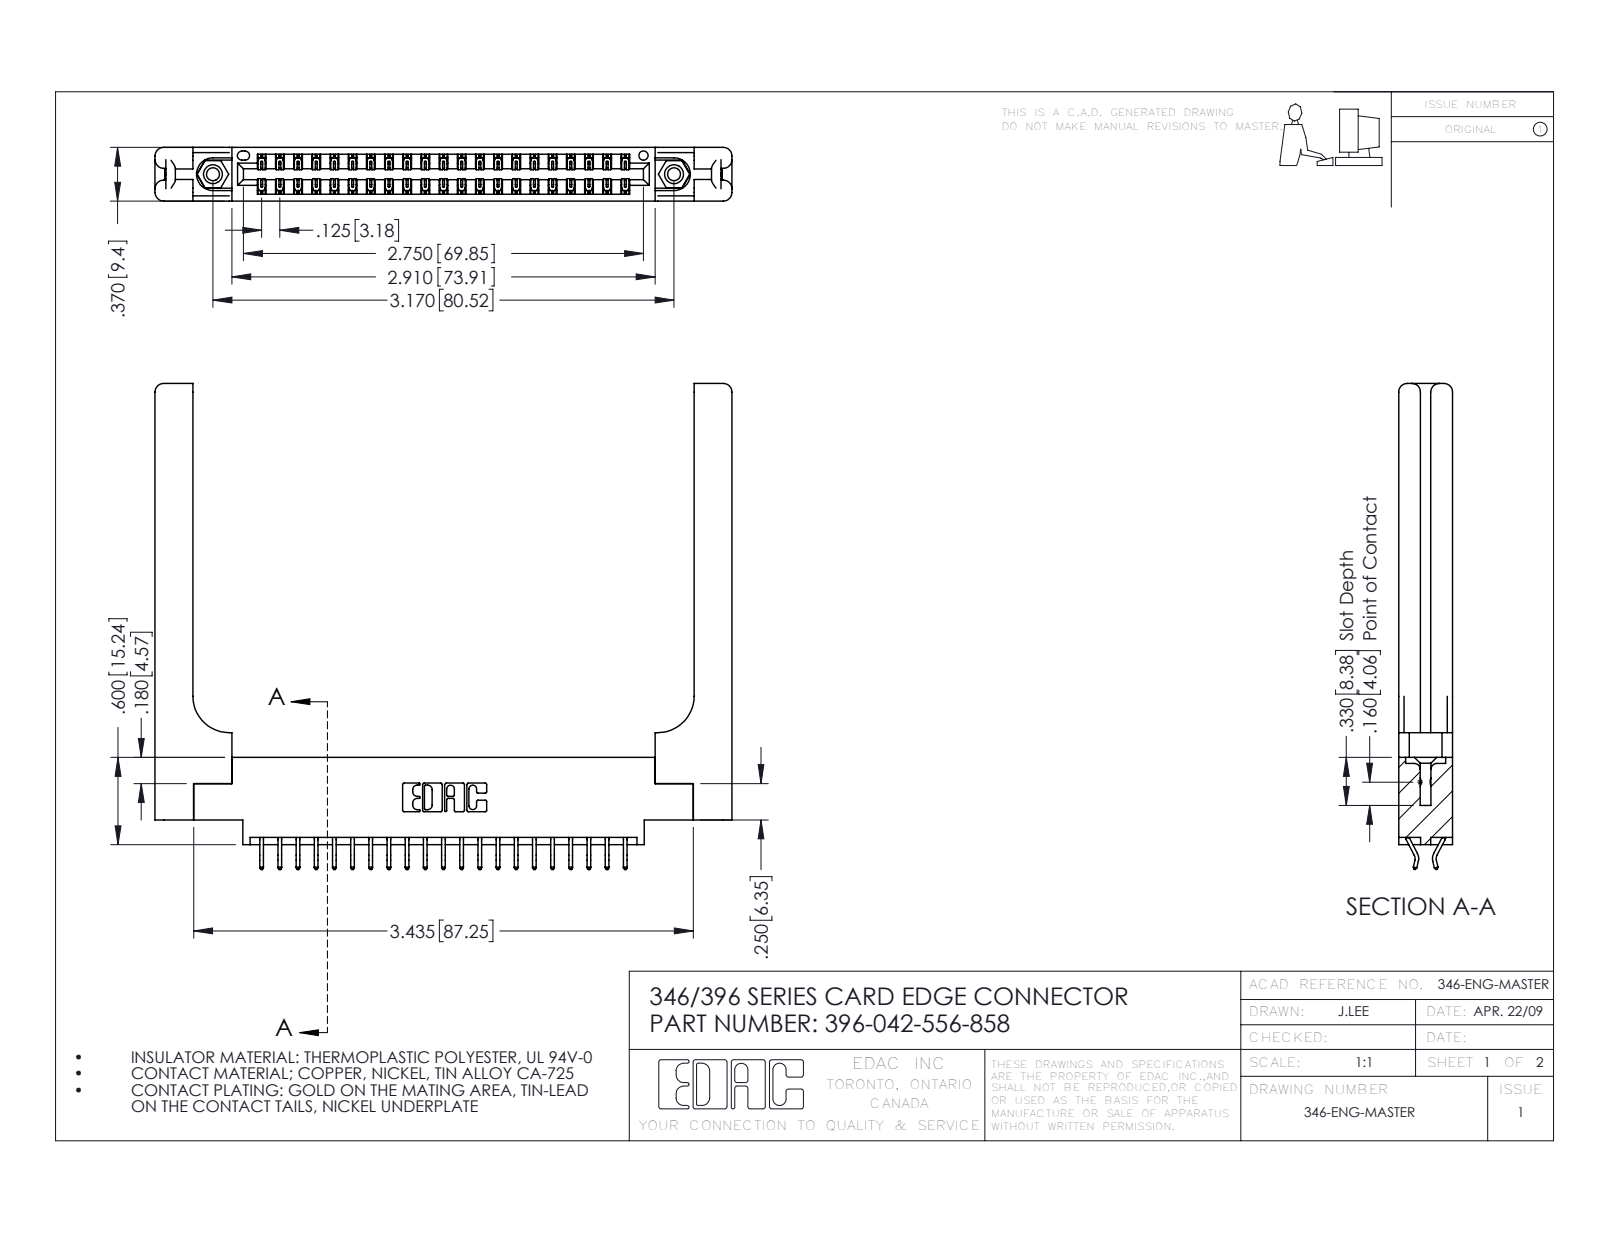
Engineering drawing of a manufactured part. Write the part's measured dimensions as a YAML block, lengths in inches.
part_name: "345-250-001_345-250-001-102; 346 Part_0.170 Offset - 0.156 Dia-TH; 345-292-001_556 Tail; 396-042-556-858 (+1 more)"
step_written_by: "SolidWorks 2016 (CONFIG_CONTROL_DESIGN)"
units: inches
bodies: {solids: 47, faces: 2818, planar: 1866, cylindrical: 892, other: 60}
overall_size: [3.966, 3.34, 0.37]
volume: 1.037
surface_area: 27.66
round_holes:
  - {diameter: 0.089, count: 2}
  - {diameter: 0.125, count: 2}
  - {diameter: 0.156, count: 2}
  - {diameter: 0.064, count: 1}
round_bosses_or_shafts:
  - {diameter: 0.155, count: 2}
partial_cylinders:
  - {radius: 0.006, count: 63}
  - {radius: 0.01, count: 22}
  - {radius: 0.06, count: 16}
  - {radius: 0.007, count: 6}
  - {radius: 0.031, count: 6}
  - {radius: 0.026, count: 3}
  - {radius: 0.01, count: 2}
  - {radius: 0.014, count: 2}
face_to_face_distances: [0.37, 0.072, 0.148, 0.15, 0.048, 0.322, 0.25, 0.025, 0.077, 0.298]
hole_center_spacings: [0.246, 2.963, 3.17]
